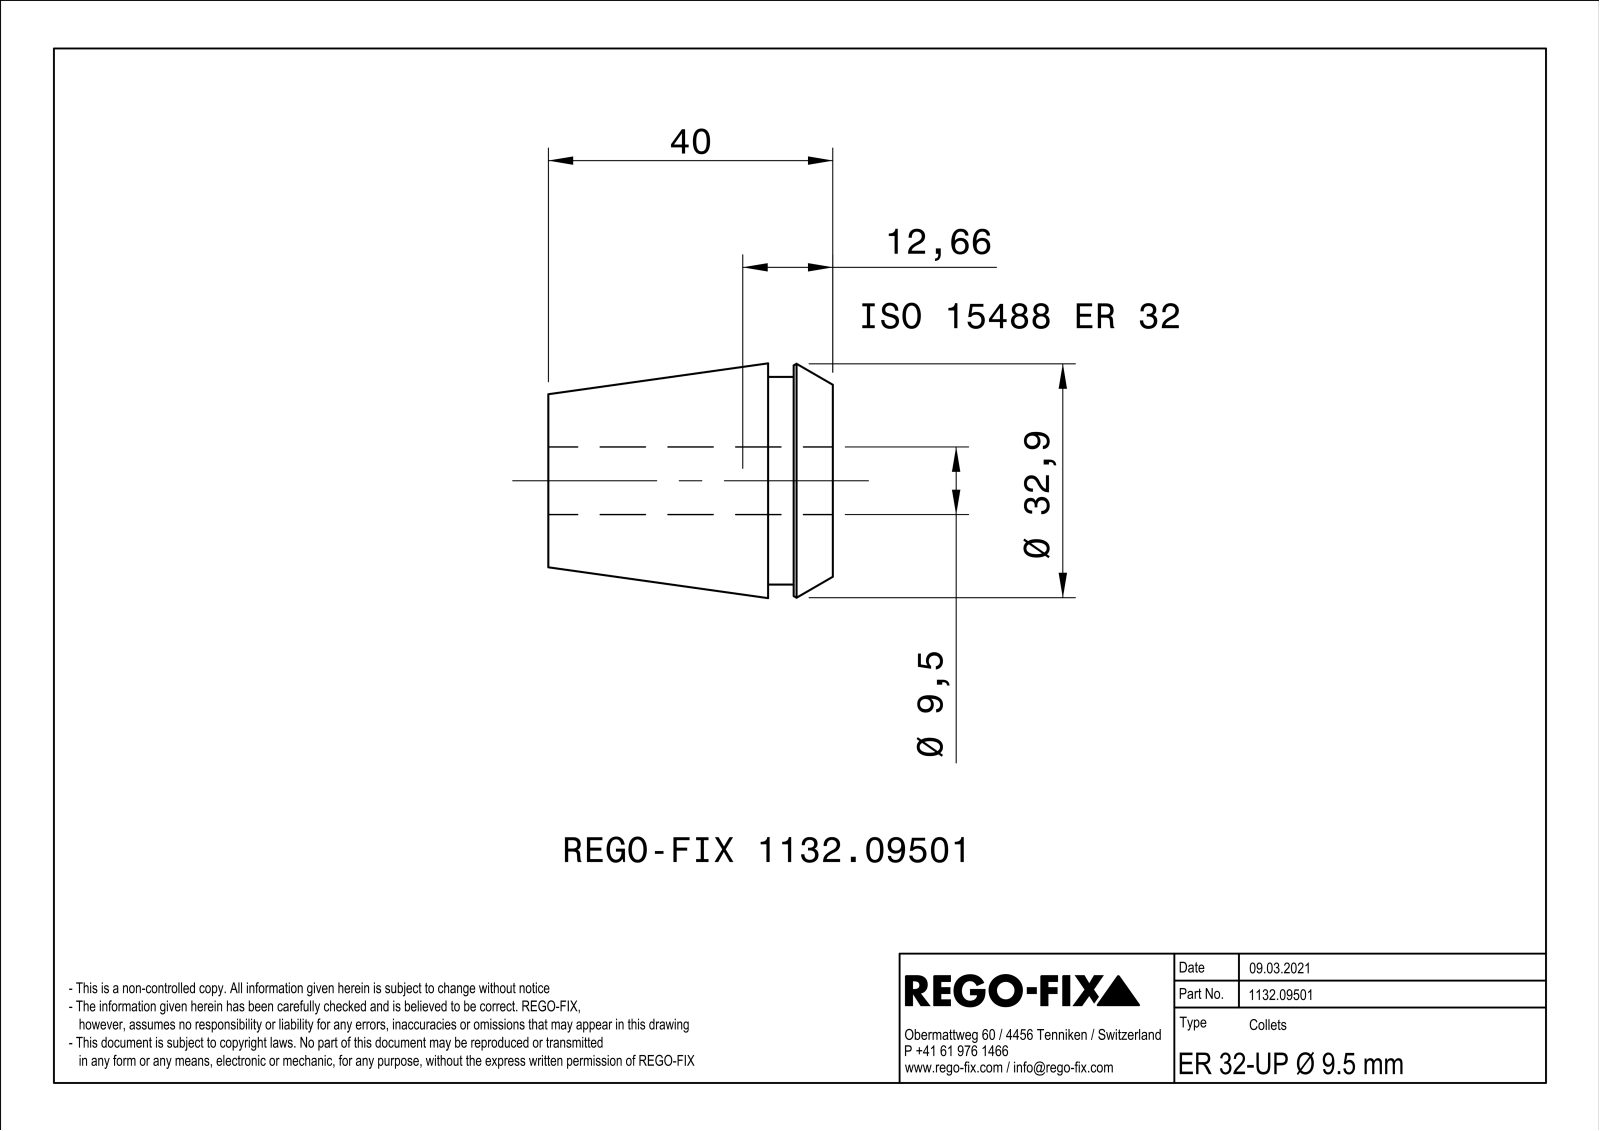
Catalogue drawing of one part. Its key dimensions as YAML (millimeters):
part_name: "NOCUT"
step_written_by: "SIEMENS PLM Software Solid Edge ST10 (AUTOMOTIVE_DESIGN)"
units: millimeters
bodies: {solids: 1, faces: 209, planar: 88, cylindrical: 41, other: 80}
overall_size: [40, 32.98, 32.98]
volume: 18066
surface_area: 16010
round_holes:
  - {diameter: 9.5, count: 1}
round_bosses_or_shafts:
  - {diameter: 29.2, count: 1}
partial_cylinders:
  - {radius: 0.4, count: 20}
face_to_face_distances: [1, 40, 9.1, 30.9, 5.5, 3.6, 34.5, 6, 0.5, 3.1]
